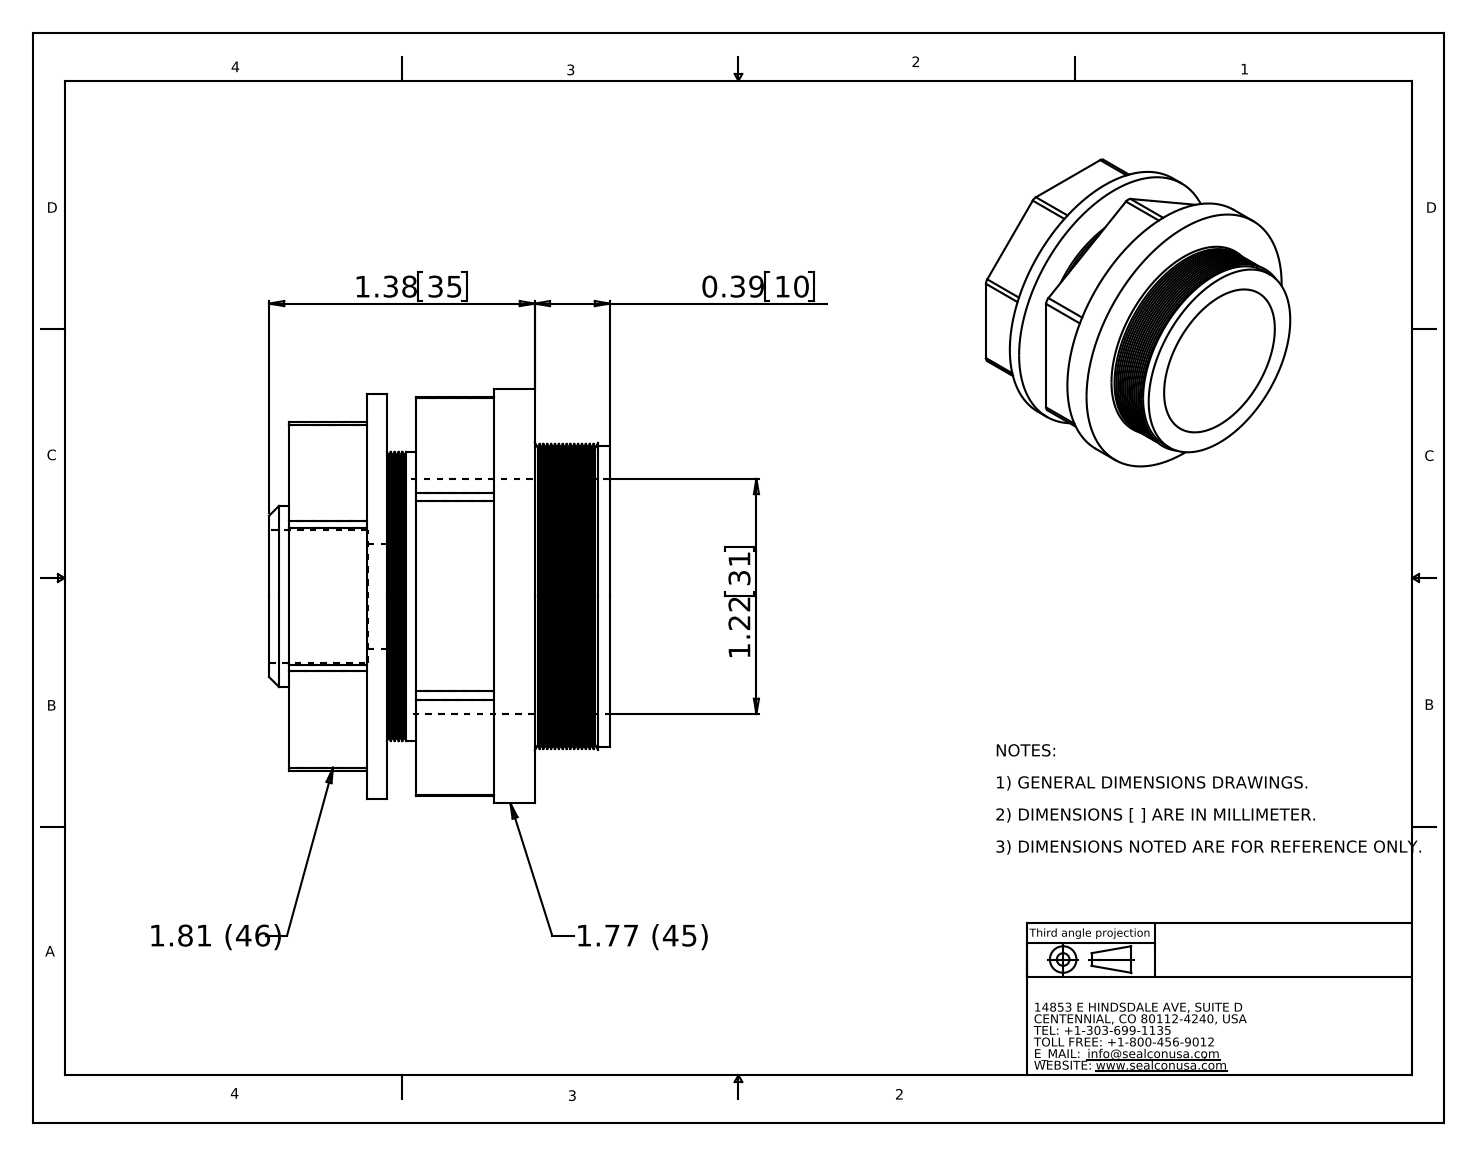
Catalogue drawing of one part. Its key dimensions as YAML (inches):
part_name: "ST29AA-BK"
step_written_by: "SolidWorks 2008 (CONFIG_CONTROL_DESIGN)"
units: inches
bodies: {solids: 2, faces: 141, planar: 25, cylindrical: 30, other: 86}
overall_size: [2.15, 2.15, 1.77]
volume: 2.888
surface_area: 29.05
round_holes:
  - {diameter: 0.55, count: 1}
  - {diameter: 0.687, count: 1}
  - {diameter: 1.22, count: 1}
round_bosses_or_shafts:
  - {diameter: 2.15, count: 1}
  - {diameter: 2.1, count: 1}
  - {diameter: 1.56, count: 1}
  - {diameter: 1.5, count: 1}
  - {diameter: 0.94, count: 1}
partial_cylinders:
  - {radius: 0.05, count: 14}
face_to_face_distances: [0.51, 1.81, 1.278, 0.768, 0.663, 0.153, 0.615, 0.102, 1.067, 0.557]
